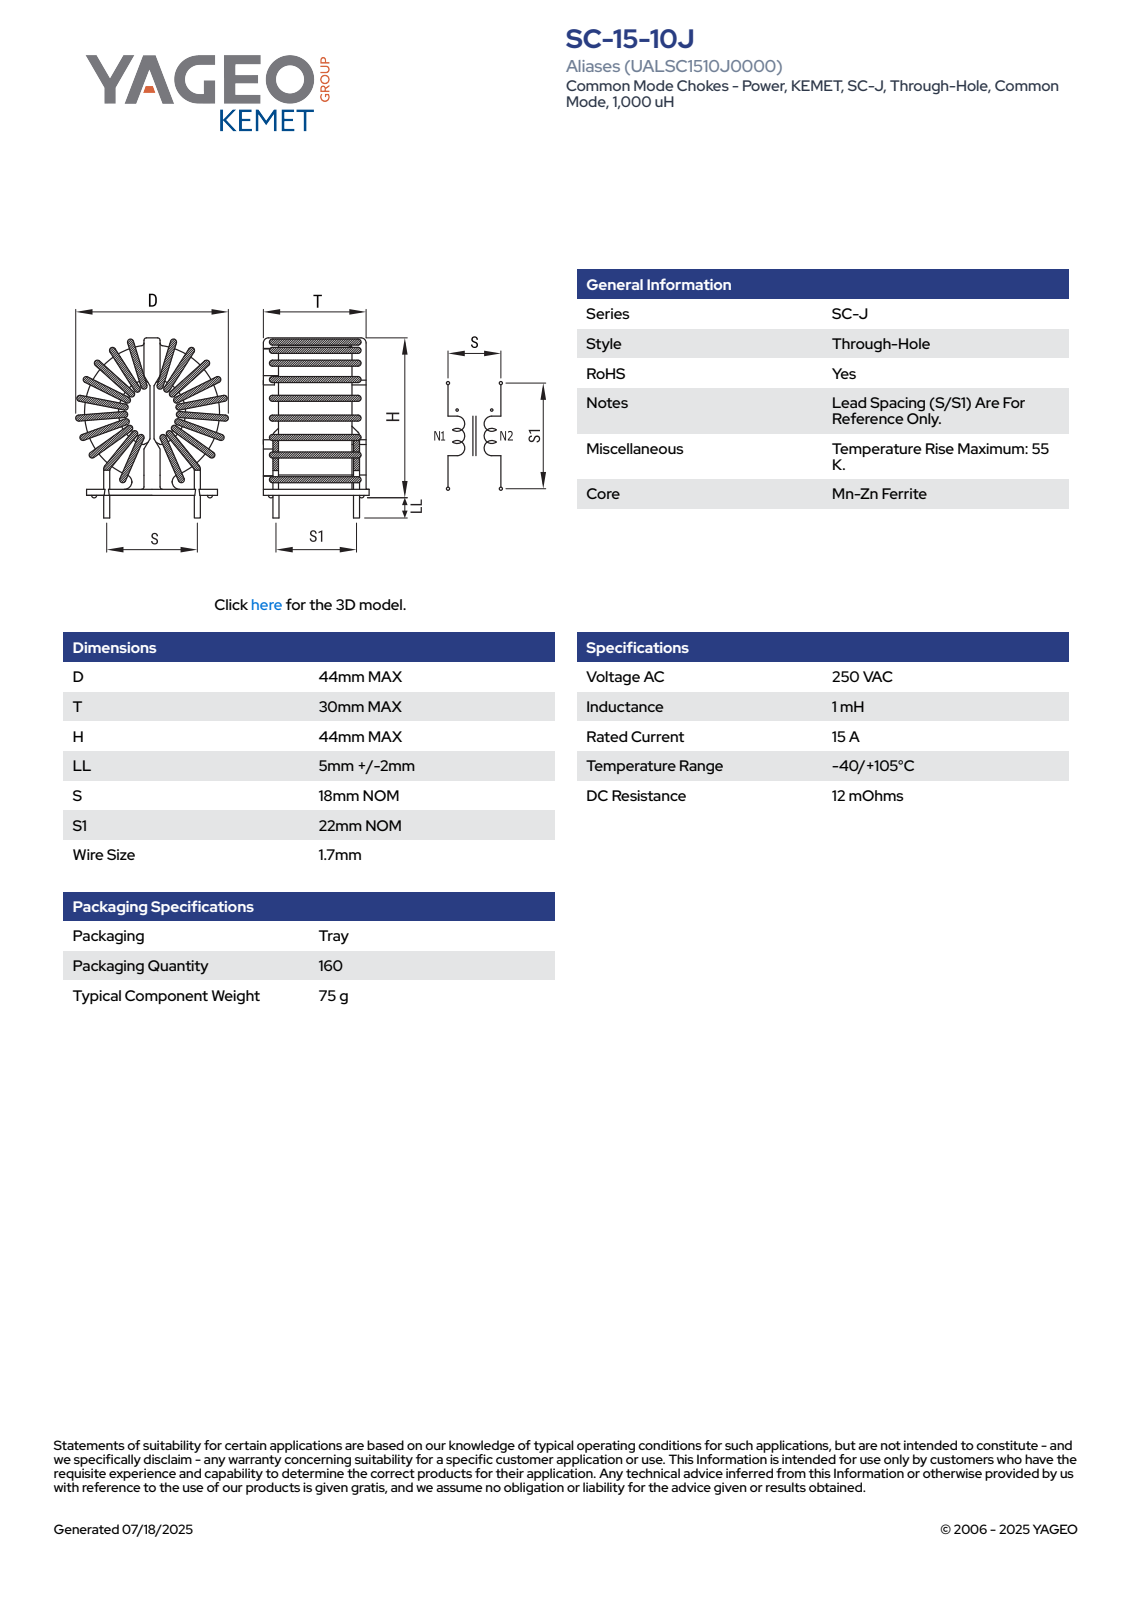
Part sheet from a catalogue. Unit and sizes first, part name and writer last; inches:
Units: inches
Overall size (bounding box): 1.909 × 1.732 × 1.181
Round holes (diameter × count): ⌀0.222 ×1
Round bosses / shafts (diameter × count): ⌀0.067 ×8, ⌀0.055 ×4
Partial cylindrical surfaces — rounded edges, fillets, slot ends (radius × count): R0.033 ×16, R0.004 ×8, R0.012 ×8, R0.039 ×8, R0.008 ×4, R0.02 ×4, R0.059 ×4, R0.126 ×4
Main face-to-face distances: 0.059, 0.866, 0.138, 0.047, 0.091, 0.043, 0.102, 0.764, 0.039, 0.728
Volume: 1.655 in³ · Surface area: 20.3 in²
Bodies: 1 solid, 429 faces (223 planar, 138 cylindrical, 68 other)
Part name (STEP PRODUCT): SC-15-10J
STEP written by: SolidWorks 2018 (AUTOMOTIVE_DESIGN)
